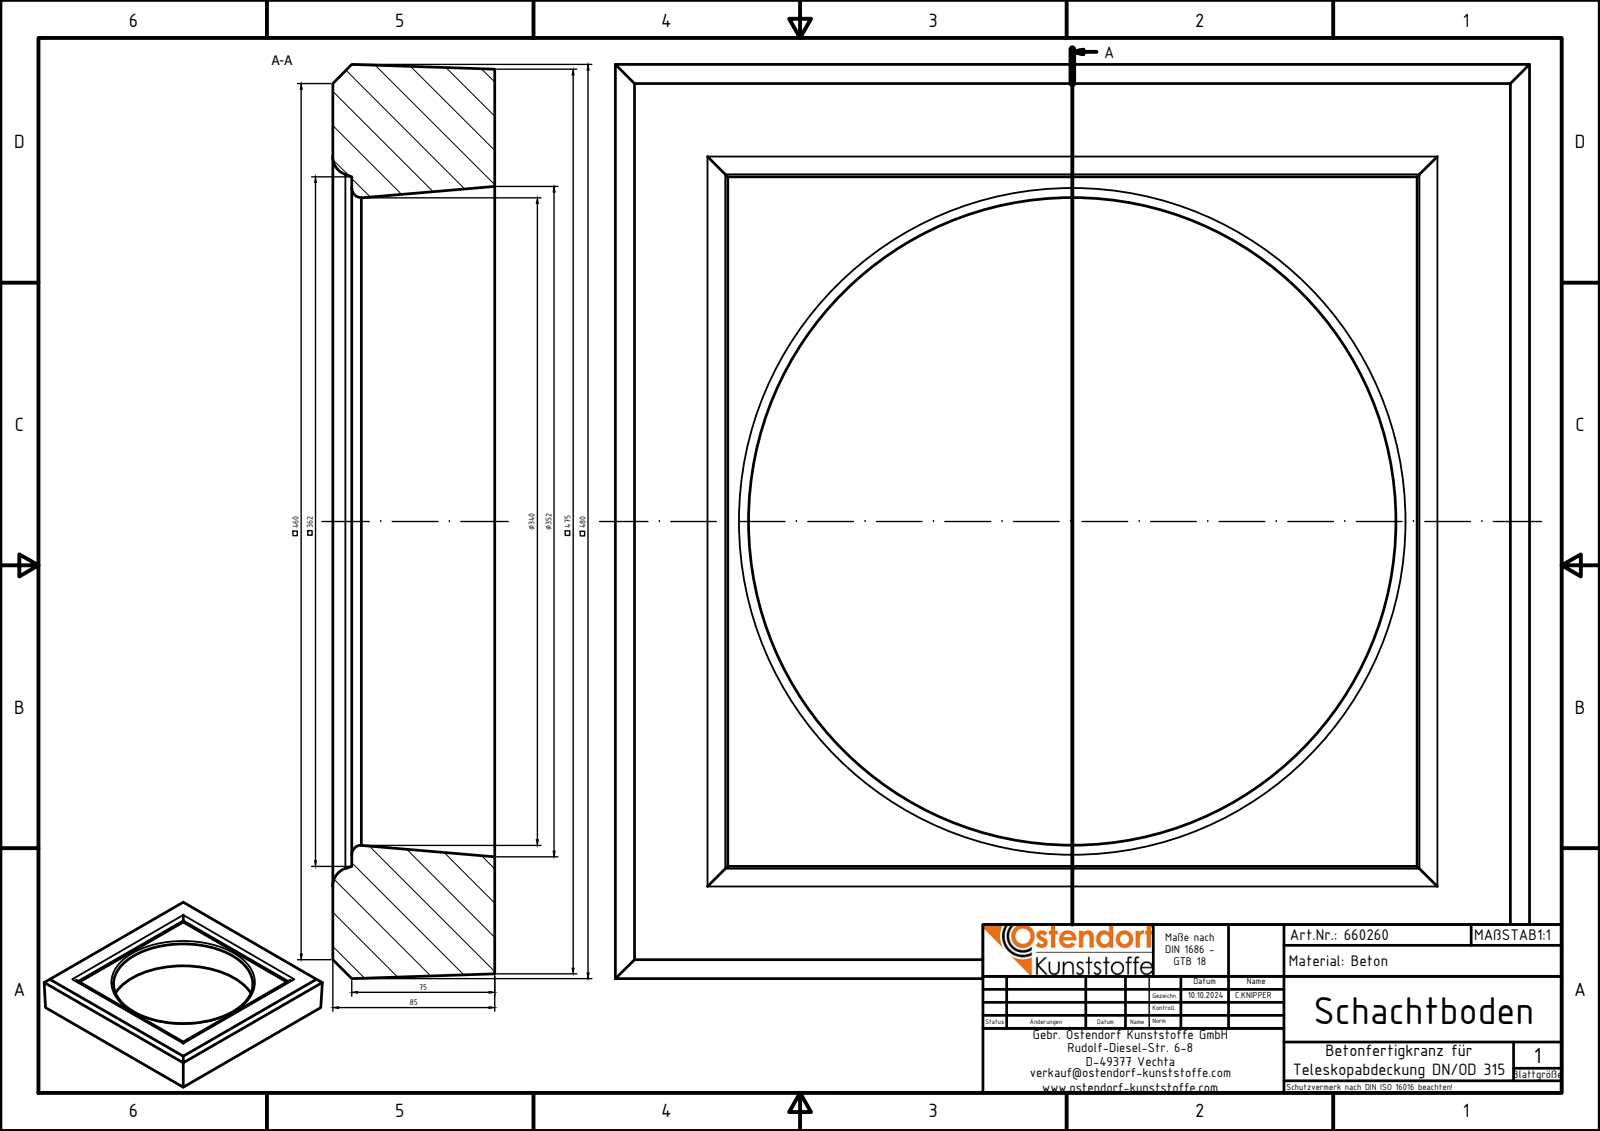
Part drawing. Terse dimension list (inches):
name: 660260z
written by: Autodesk Inventor 2024 (AUTOMOTIVE_DESIGN)
unit: in
bodies: 1 solid, 21 faces (15 planar, 4 cylindrical, 2 other)
size: 18.898 × 18.898 × 3.346
volume: 666.4 in³; area: 784.4 in²
rounds: 4× R0.394
face distances: 3.346, 2.953, 0.394
